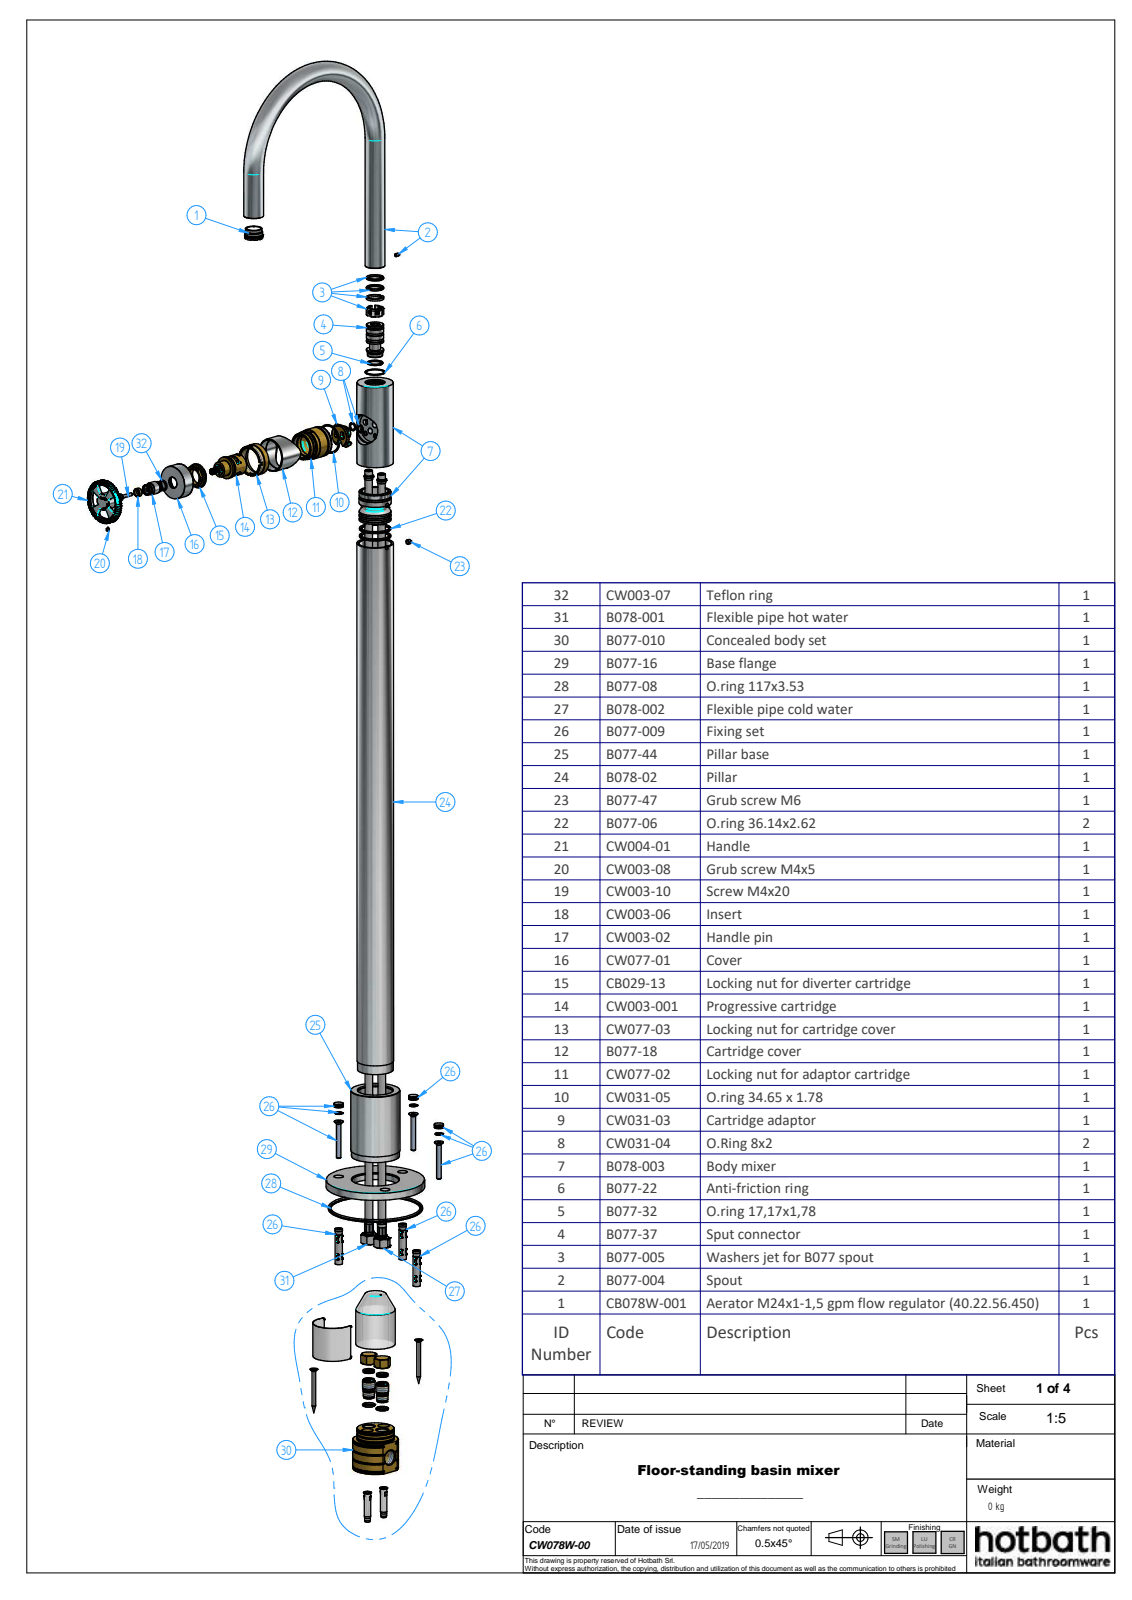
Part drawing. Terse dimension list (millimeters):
name: CW078W-00; B078-002; parte superiore; oring7.65x1.78.1 (+8 more)
written by: ST-DEVELOPER v16.7 (AUTOMOTIVE_DESIGN)
unit: mm
bodies: 87 solids, 3541 faces (990 planar, 1124 cylindrical, 1427 other)
size: 1315.2 × 302.75 × 129.5
volume: 1 014 000 mm³; area: 718 662 mm²
holes: 9× ⌀5, 4× ⌀7.5, 4× ⌀8, 4× ⌀9, 4× ⌀14.95, 3× ⌀6.4, 3× ⌀8.7, 3× ⌀10.5, 3× ⌀11, 3× ⌀12.5, 3× ⌀15, 2× ⌀4
bosses: 5× ⌀10.5, 5× ⌀10, 4× ⌀9.6, 4× ⌀8, 4× ⌀6, 3× ⌀14.4, 3× ⌀12.2, 3× ⌀11.7
rounds: 118× R0.2, 112× R0.6, 112× R7.9, 24× R1.25, 21× R3, 20× R0.1, 20× R1, 11× R2.5
face distances: 9.3, 4.5, 4.8, 92, 10, 0.7, 5.2, 61, 818, 3.2
hole spacings: 19.21, 19.53, 15.81, 50, 0.5, 8.6, 10.39, 12
